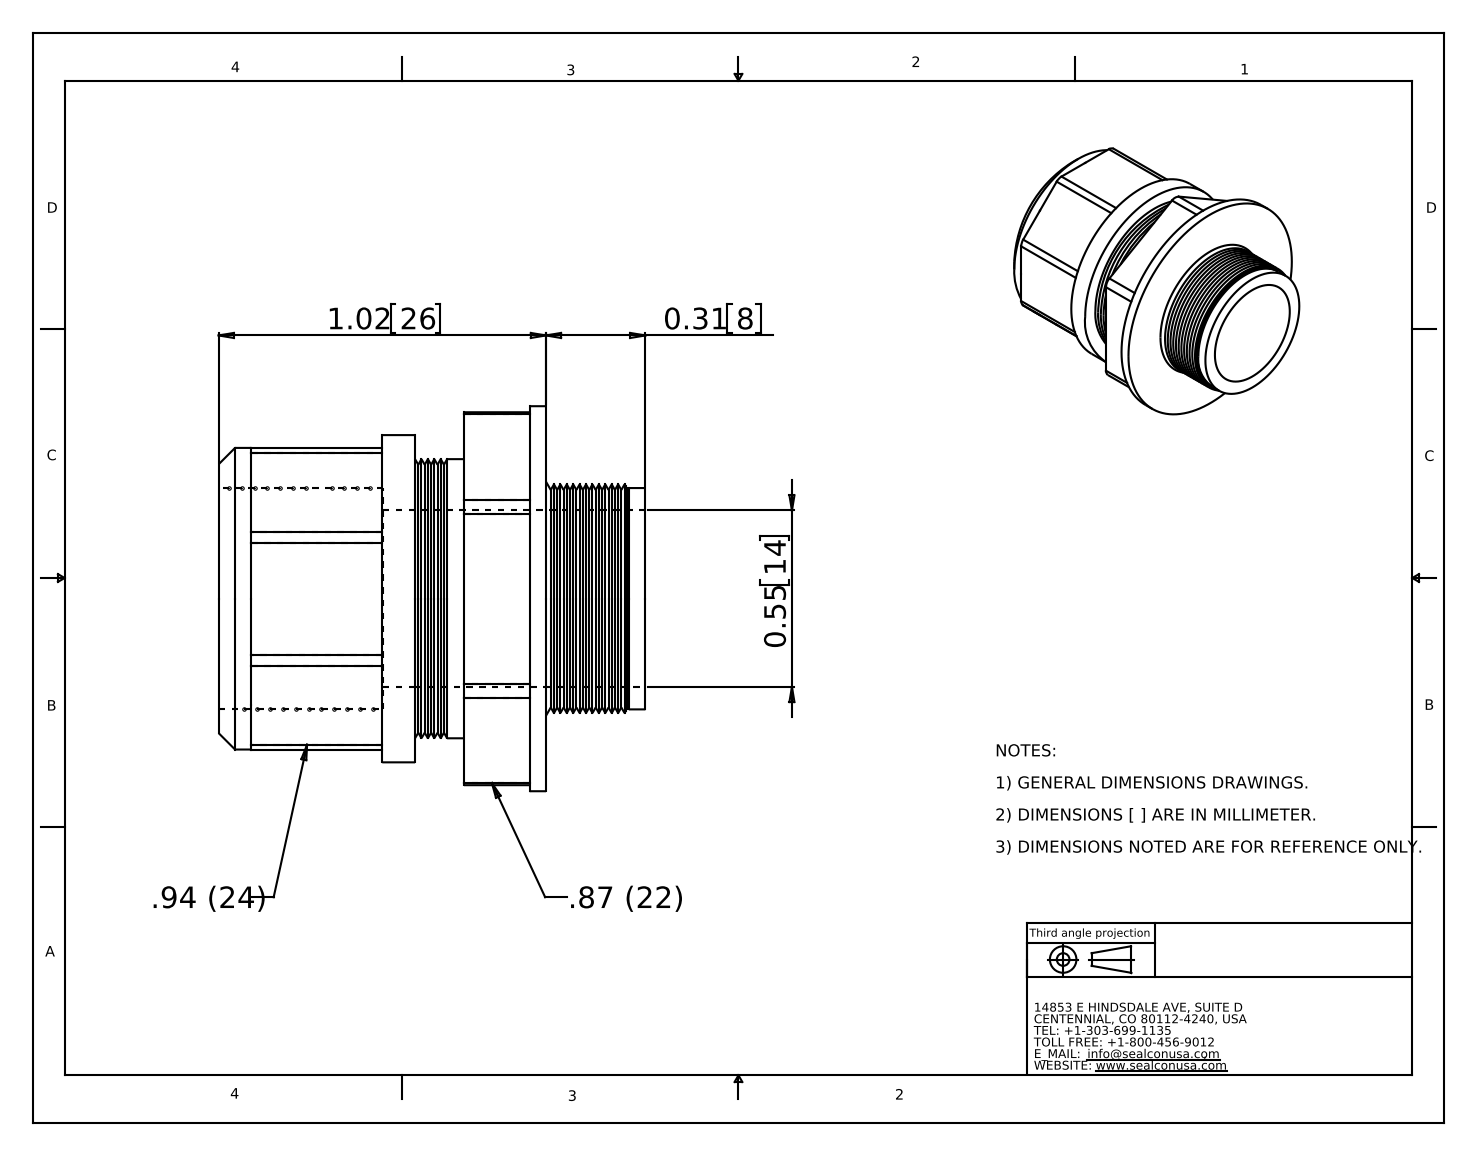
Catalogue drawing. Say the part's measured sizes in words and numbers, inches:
The part is named "ST11AA-BK". Its 3-D file was written by "SolidWorks 2007 (AUTOMOTIVE_DESIGN)". It is 2 solids with 140 faces: 32 planar, 32 cylindrical and 76 other. Overall it measures 1.33 by 1.2 by 1.2 inches. Its volume is 0.512 cubic inches and its surface area 10.05 square inches. Round holes: 1 of diameter 0.55, 1 of diameter 0.687. Round bosses or shafts: 1 of diameter 1.2, 1 of diameter 1.02, 1 of diameter 0.94, 1 of diameter 0.87, 1 of diameter 0.69. Partial cylindrical surfaces (rounded edges, fillets, slot ends): 14 of radius 0.05. The main face-to-face distances are 0.408, 0.94, 0.255, 1.02, 0.153, 0.357, 0.204, 0.051, 0.04, 0.98.
